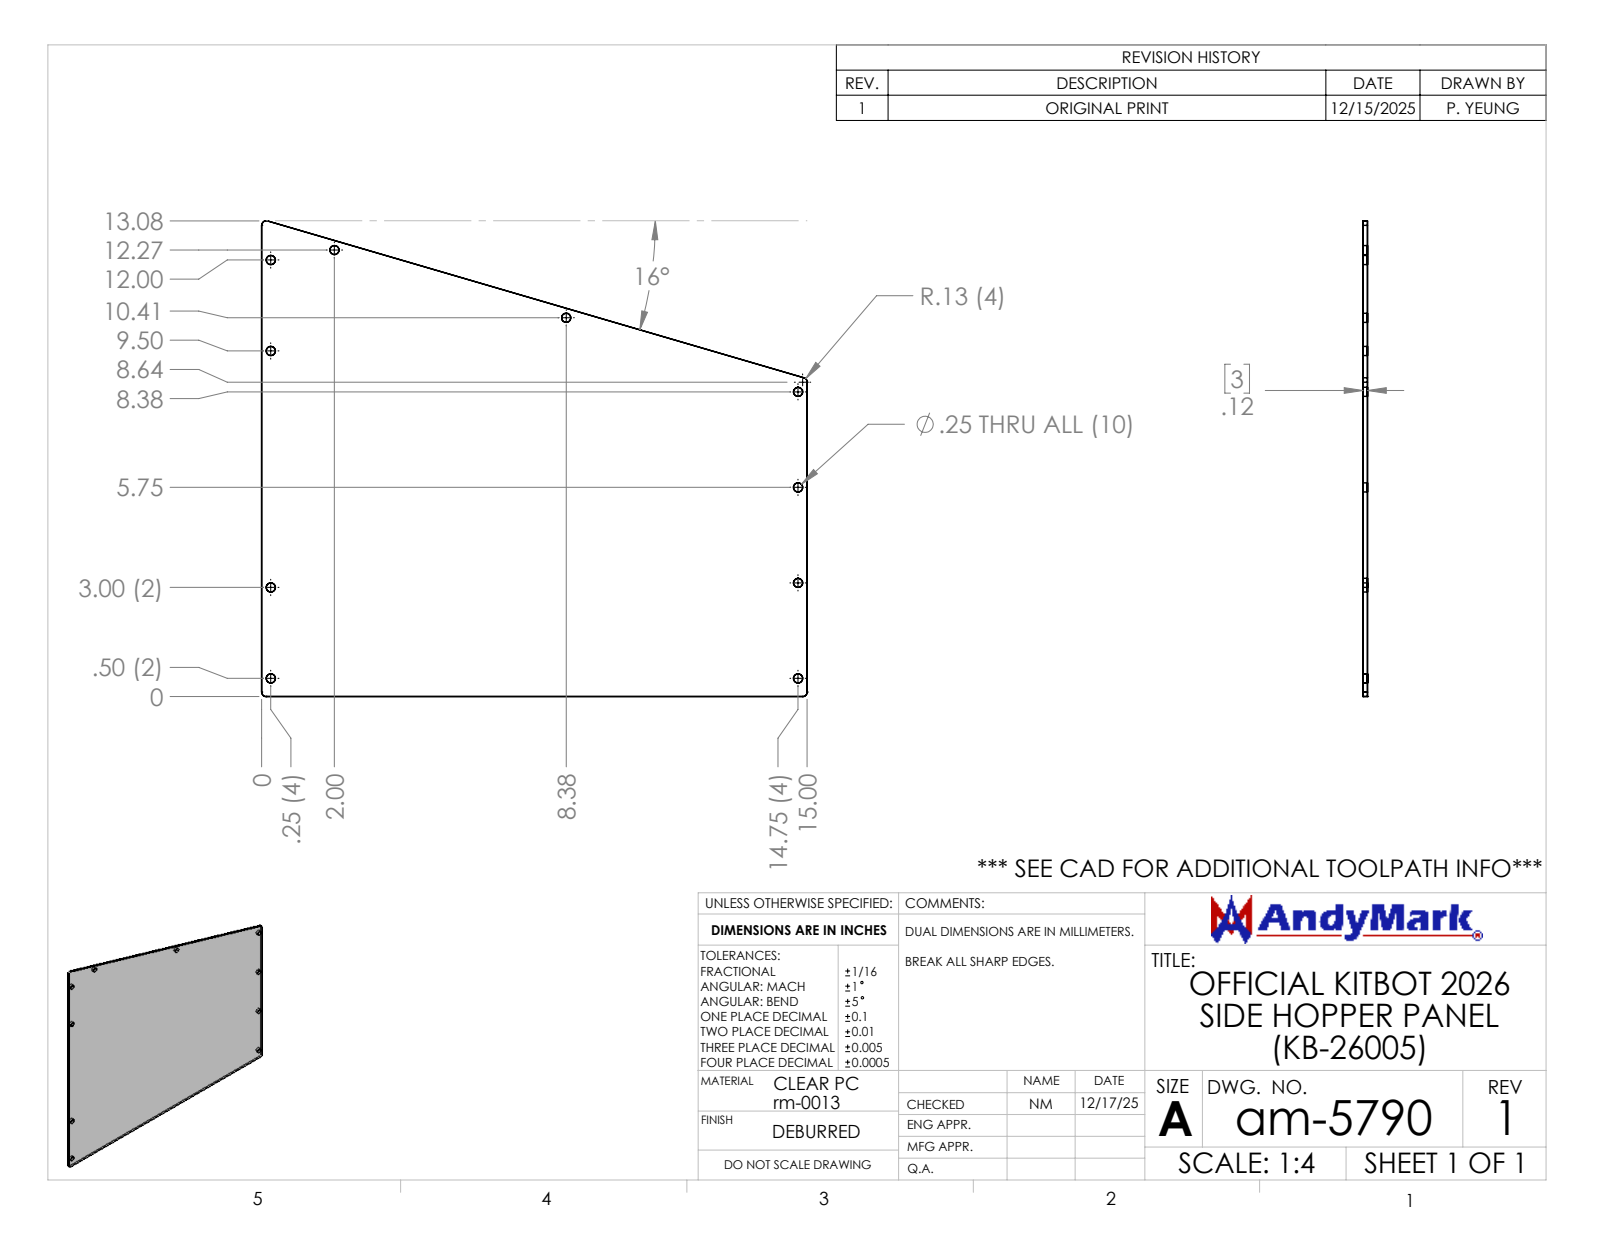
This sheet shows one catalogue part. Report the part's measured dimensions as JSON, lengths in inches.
{"part_name": "am-5790 Side Hopper Panel (KB-26005)", "step_written_by": "SolidWorks 2024 (AUTOMOTIVE_DESIGN)", "units": "inches", "bodies": {"solids": 1, "faces": 30, "planar": 6, "cylindrical": 24, "other": 0}, "overall_size": [15, 13.077, 0.118], "volume_in3": 19.3, "surface_area_in2": 333.9, "round_holes": [[0.25, 10]], "partial_cylinders_radius": [[0.125, 4]], "face_to_face_distances": [0.118, 15], "hole_center_spacings": [2.5, 2.625, 9, 1.771, 2.625, 3.28, 5.25, 5.25]}
